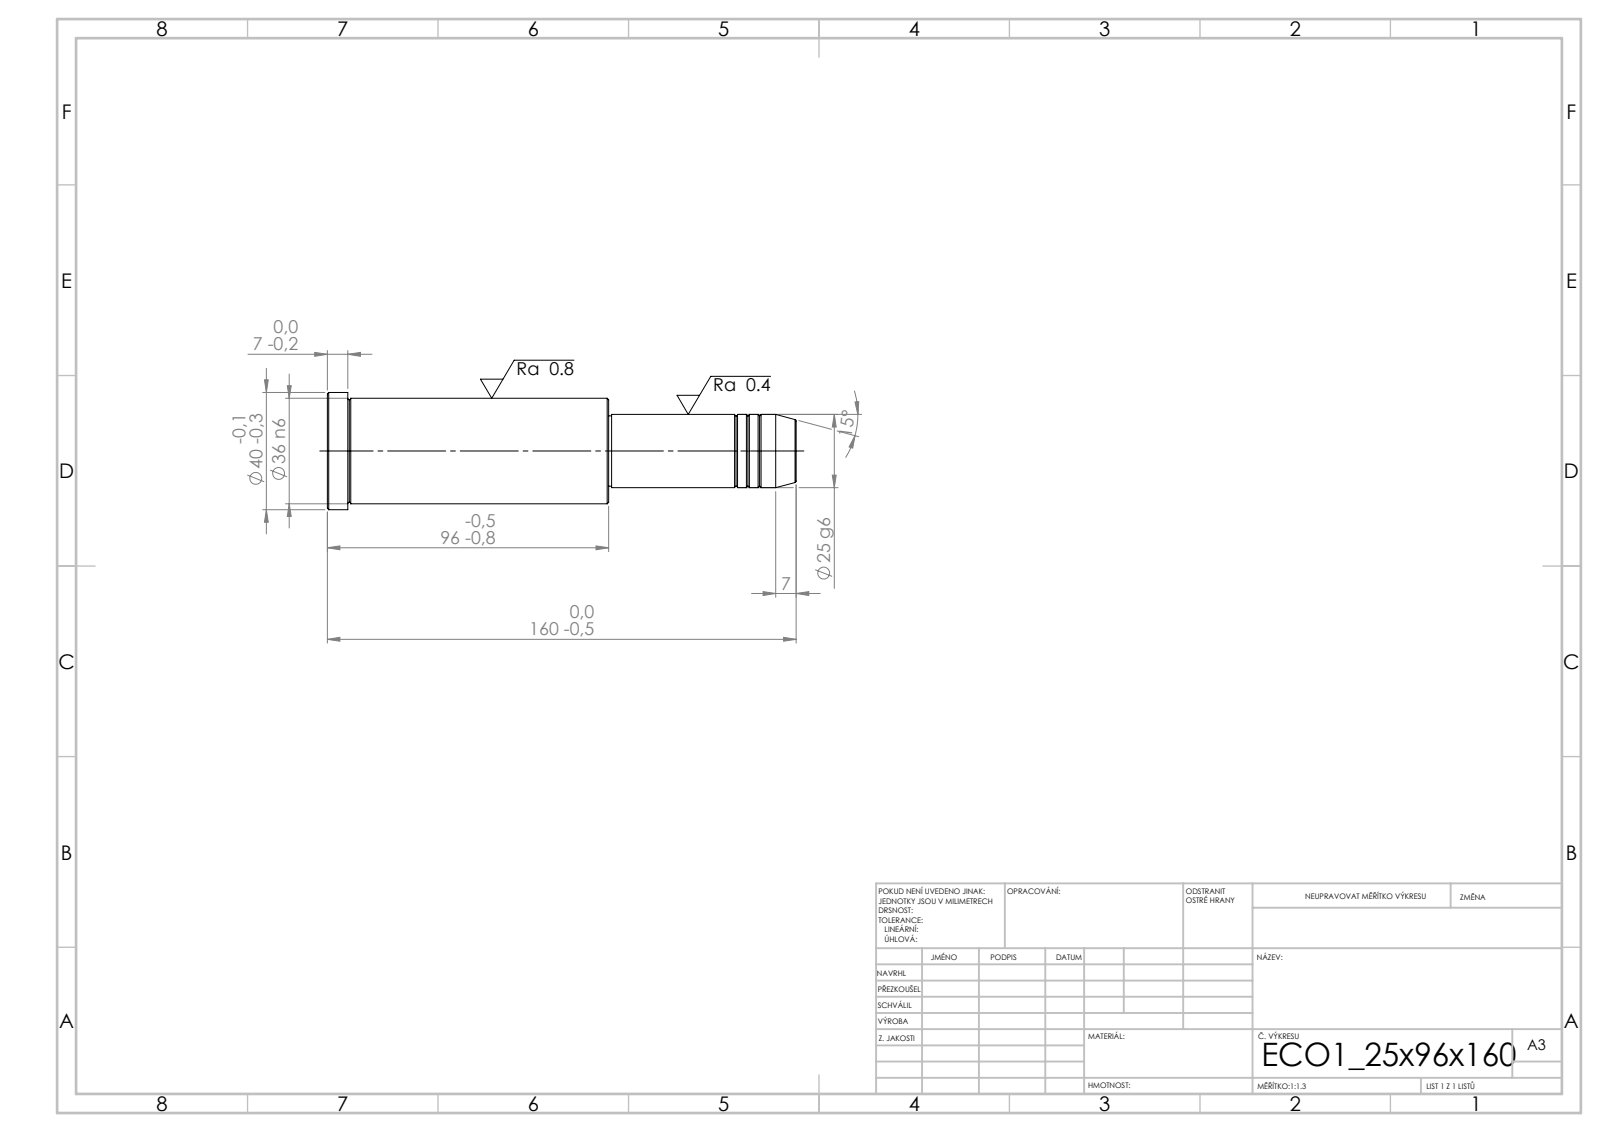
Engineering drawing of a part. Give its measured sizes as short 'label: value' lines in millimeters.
written by: SolidWorks 2019 (CONFIG_CONTROL_DESIGN)
unit: mm
bodies: 1 solid, 43 faces (5 planar, 14 cylindrical, 24 other)
size: 160 × 40 × 40
volume: 130 109 mm³; area: 18 508 mm²
bosses: 1× ⌀40, 1× ⌀36, 1× ⌀25, 1× ⌀24
face distances: 96, 64, 160, 153, 89, 7, 63, 1, 90, 97
